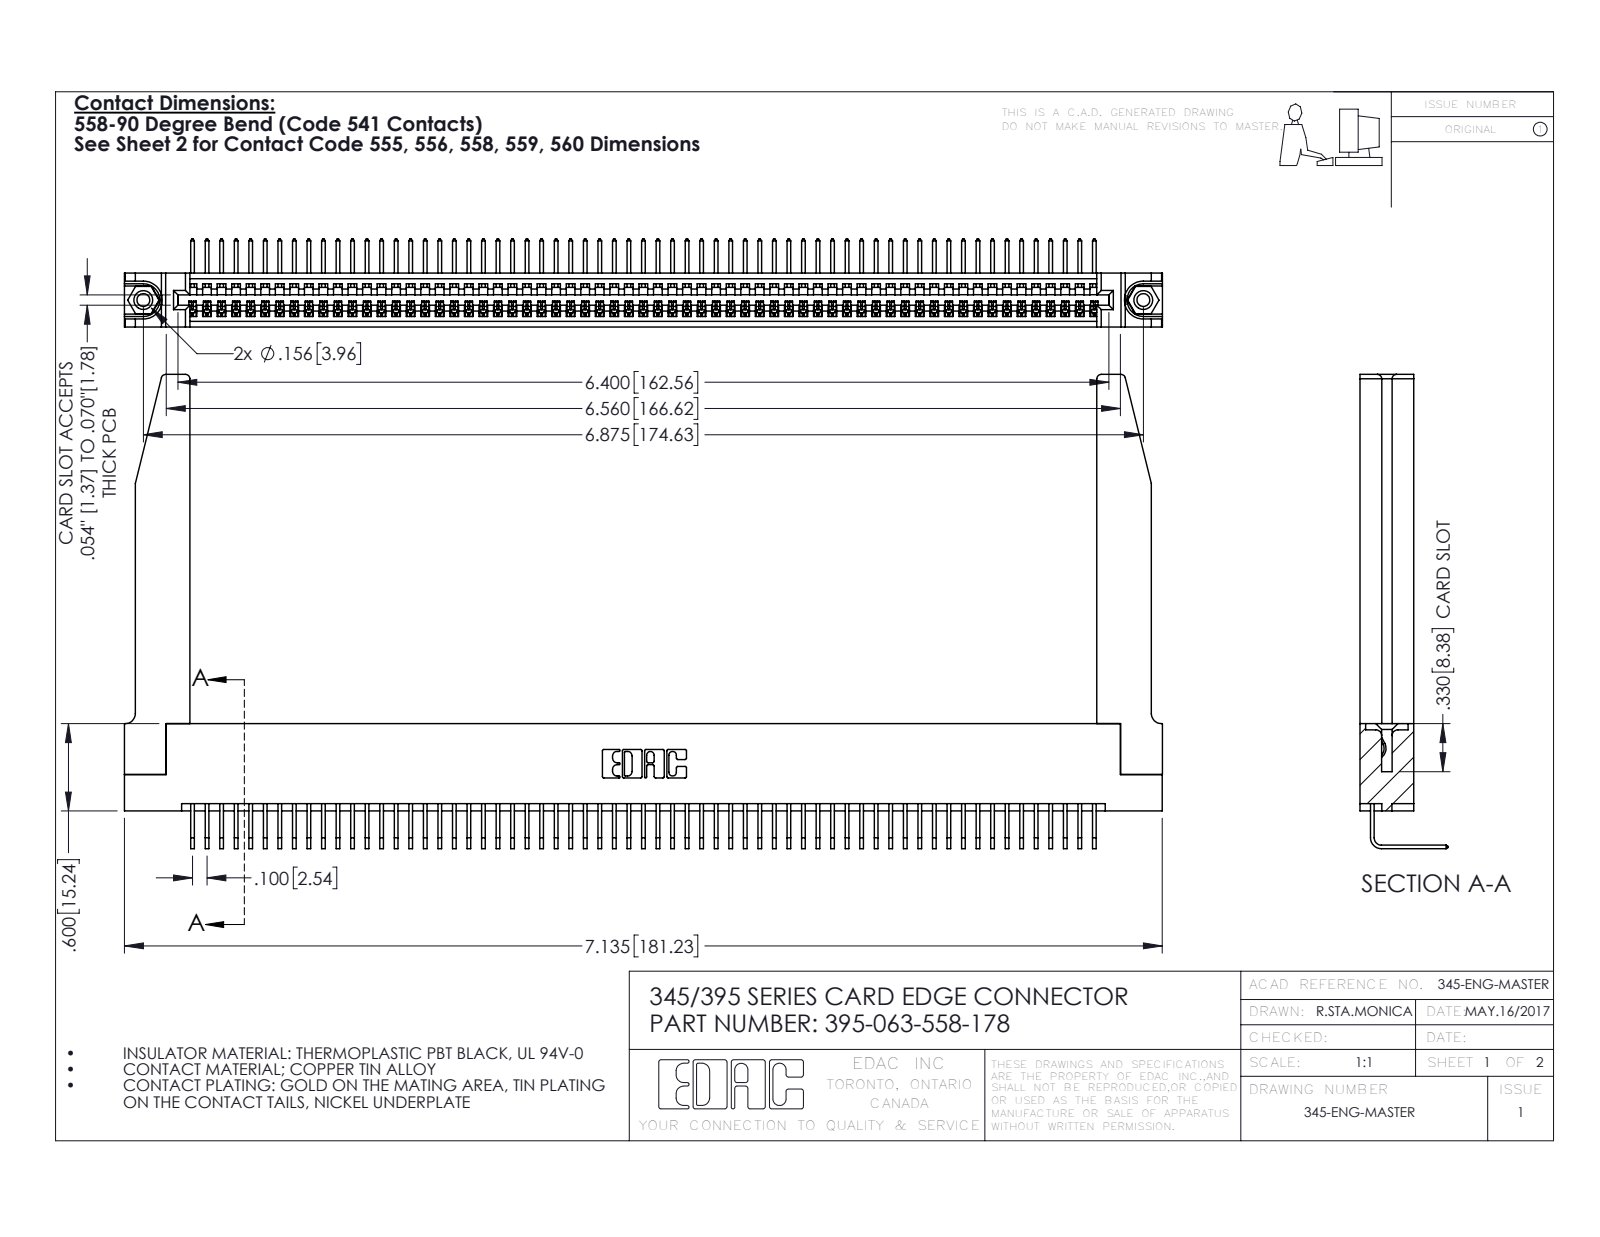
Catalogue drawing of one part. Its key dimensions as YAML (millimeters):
part_name: "395-063-558-178; 345-292-001_558 Tail - 2; 345-250-001_345-250-001-102; 345-220-078_345-220-078 (+1 more)"
step_written_by: "SolidWorks 2016 (CONFIG_CONTROL_DESIGN)"
units: millimeters
bodies: {solids: 68, faces: 4140, planar: 2868, cylindrical: 1220, other: 52}
overall_size: [181.3, 82.8, 15.4]
volume: 25370
surface_area: 31750
round_holes:
  - {diameter: 2.3, count: 2}
  - {diameter: 3.2, count: 2}
  - {diameter: 4, count: 2}
  - {diameter: 1.6, count: 1}
round_bosses_or_shafts:
  - {diameter: 3.9, count: 2}
partial_cylinders:
  - {radius: 0.2, count: 126}
  - {radius: 0.3, count: 22}
  - {radius: 0.8, count: 8}
  - {radius: 0.2, count: 6}
  - {radius: 0.8, count: 6}
  - {radius: 0.7, count: 3}
  - {radius: 0.8, count: 2}
  - {radius: 1, count: 2}
face_to_face_distances: [1.8, 9.4, 7.6, 5.1, 2.5, 6.9, 0.6, 5.7, 3.8, 3.8]
hole_center_spacings: [6.9, 168.6, 174.6]
